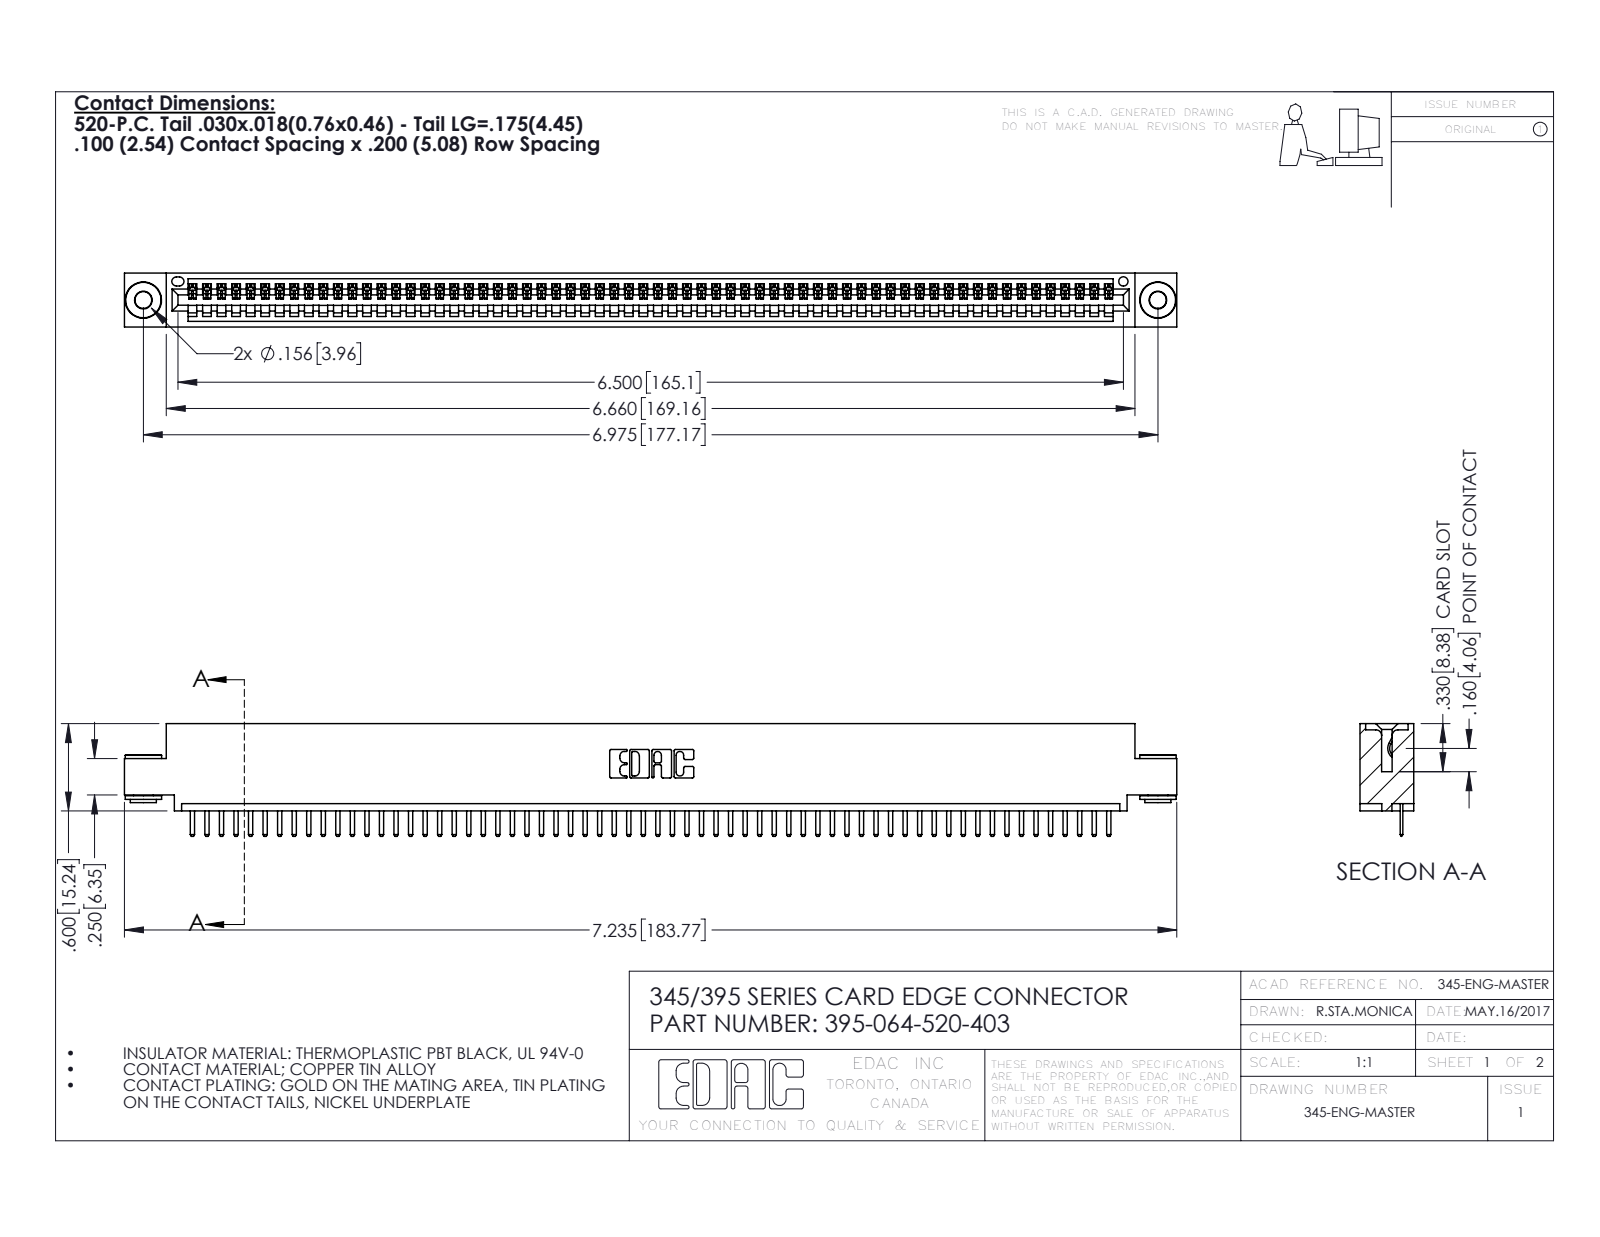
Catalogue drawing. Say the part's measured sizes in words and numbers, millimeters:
The part is named "345-250-002_345-250-002-102; 395-064-520-403; 345 Part_0.110 Offset - 0.156 Dia-TH; 345-292-001_345-293-120". Its 3-D file was written by "SolidWorks 2016 (CONFIG_CONTROL_DESIGN)". It is 67 solids with 4136 faces: 2782 planar, 1346 cylindrical and 8 other. Overall it measures 183.8 by 19.7 by 9.4 millimeters. Its volume is 17 400 cubic millimeters and its surface area 23 110 square millimeters. Round holes: 2 of diameter 2.9, 2 of diameter 4, 1 of diameter 1.6. Round bosses or shafts: 2 of diameter 6.4, 2 of diameter 4.6, 2 of diameter 3.5. Partial cylindrical surfaces (rounded edges, fillets, slot ends): 130 of radius 0.3, 128 of radius 0.2, 22 of radius 0.3, 6 of radius 0.2, 6 of radius 0.8, 3 of radius 0.7, 2 of radius 0.8, 2 of radius 1. The main face-to-face distances are 1.8, 7.6, 9.4, 5.1, 0.6, 2.5, 6.9, 5.7, 1.8, 3.8. The hole center spacings are 6.9, 171.2, 177.2.
